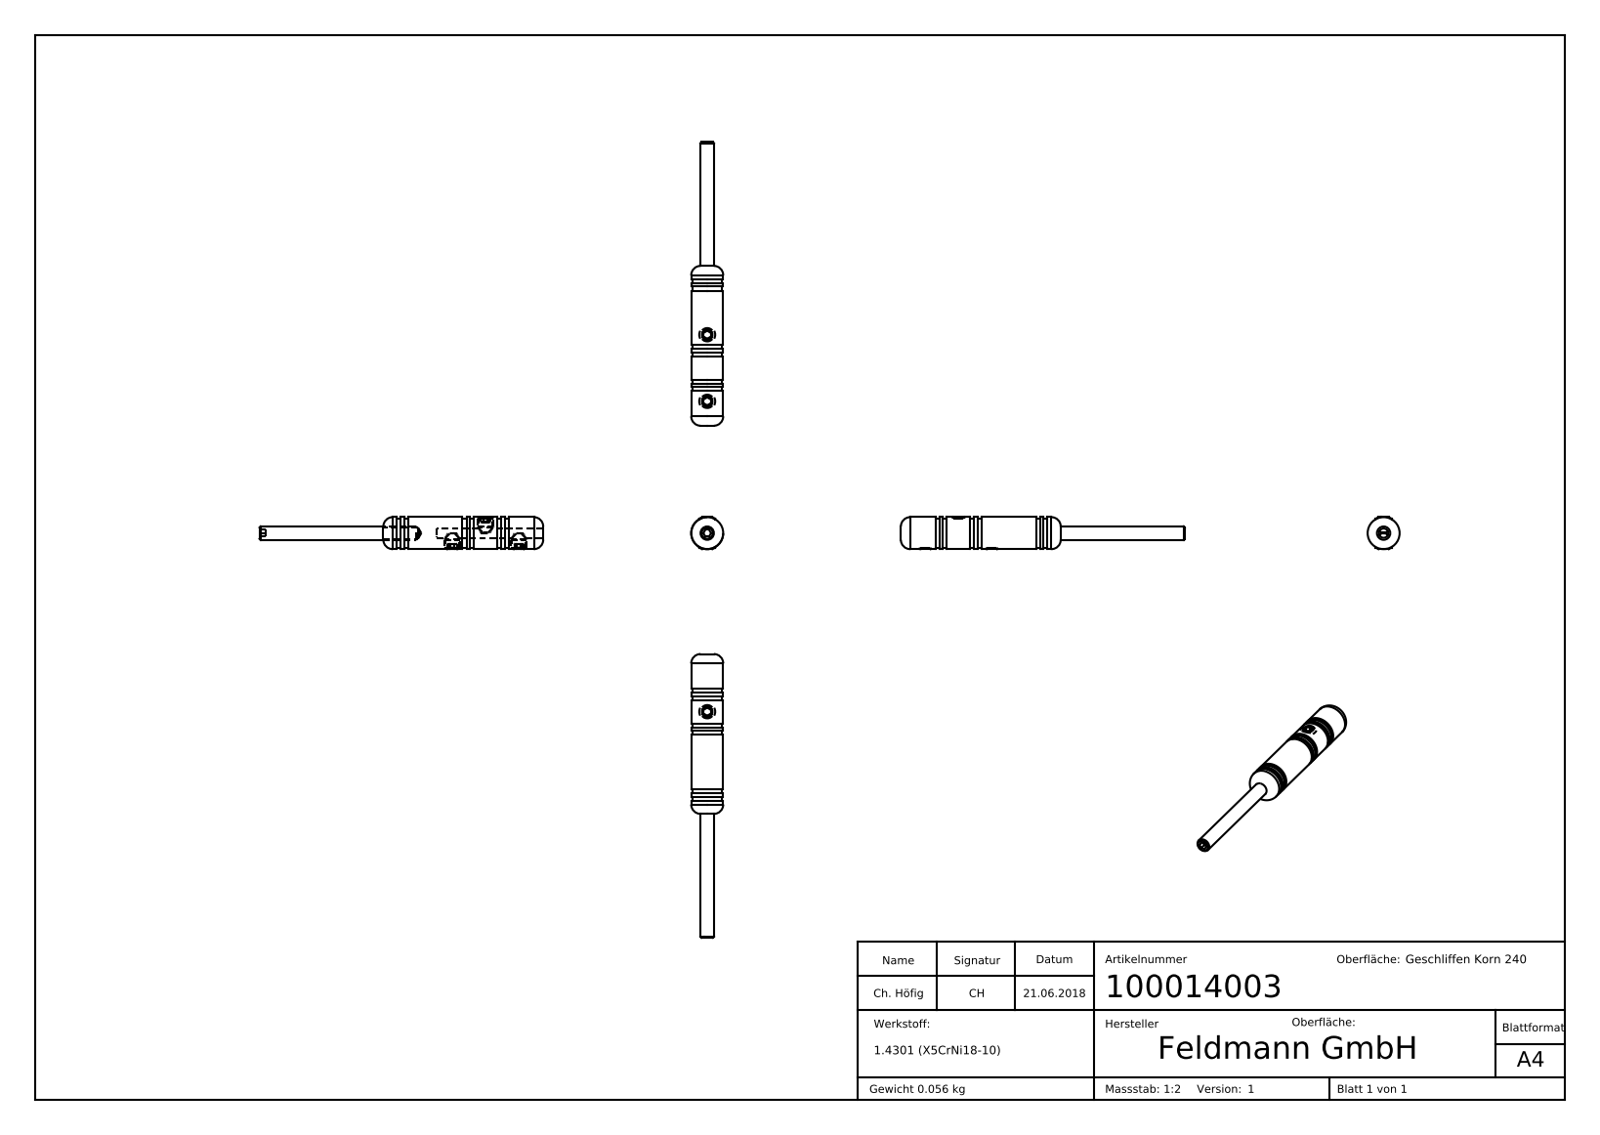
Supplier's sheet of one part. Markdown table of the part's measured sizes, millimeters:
| quantity | value |
| --- | --- |
| part name | 10001X00X Teil 1_100014003 Teil1; 100014003; DIN913_DIN913 M5x60; DIN914_DIN 914 M6x6 |
| STEP written by | SolidWorks 2015 (CONFIG_CONTROL_DESIGN) |
| units | millimeters |
| bodies | 5 solids, 440 faces (165 planar, 98 cylindrical, 177 other) |
| overall size | 106.49 × 12 × 12 |
| volume | 7 094 mm³ |
| surface area | 4 716 mm² |
| round holes (diameter × count) | 5 × 3, 3.5 × 1, 4.2 × 1 |
| round bosses / shafts (diameter × count) | 6 × 3, 12 × 1, 11 × 1, 5 × 1 |
| partial cylindrical surfaces (radius × count) | 0.2 × 50 |
| main face-to-face distances | 1.5, 2.8, 13, 24.7, 37.7, 1.3, 4.3, 14.5, 15.8, 27.5 |
| hole center spacings | 12.5, 25 |
